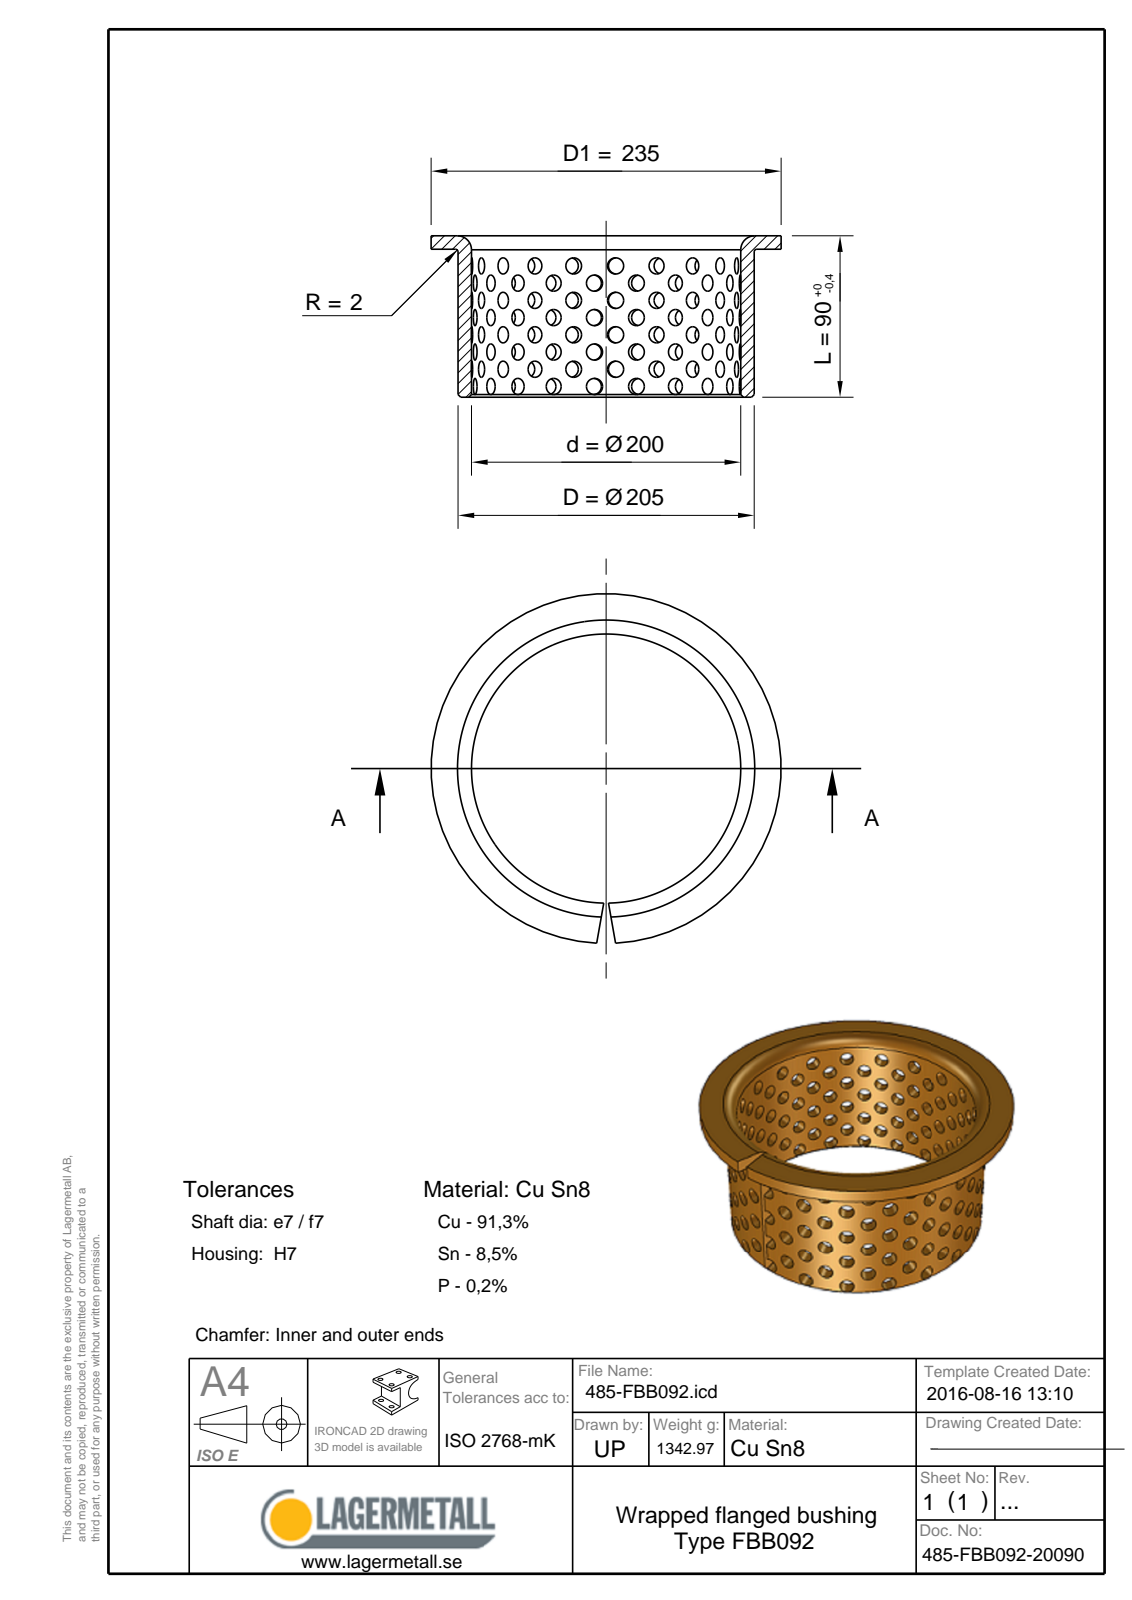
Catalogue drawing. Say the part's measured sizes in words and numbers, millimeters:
The part is named "485-FBB092-20090". Its 3-D file was written by "Spatial InterOp 3D (CONFIG_CONTROL_DESIGN)". It is 1 solid with 12 faces: 5 planar, 3 cylindrical and 4 other. Overall it measures 235 by 234.95 by 90 millimeters. Its volume is 165 799 cubic millimeters and its surface area 136 400 square millimeters. Round holes: 1 of diameter 200. Round bosses or shafts: 1 of diameter 235, 1 of diameter 205. The main face-to-face distances are 2.5, 87.5, 90.
